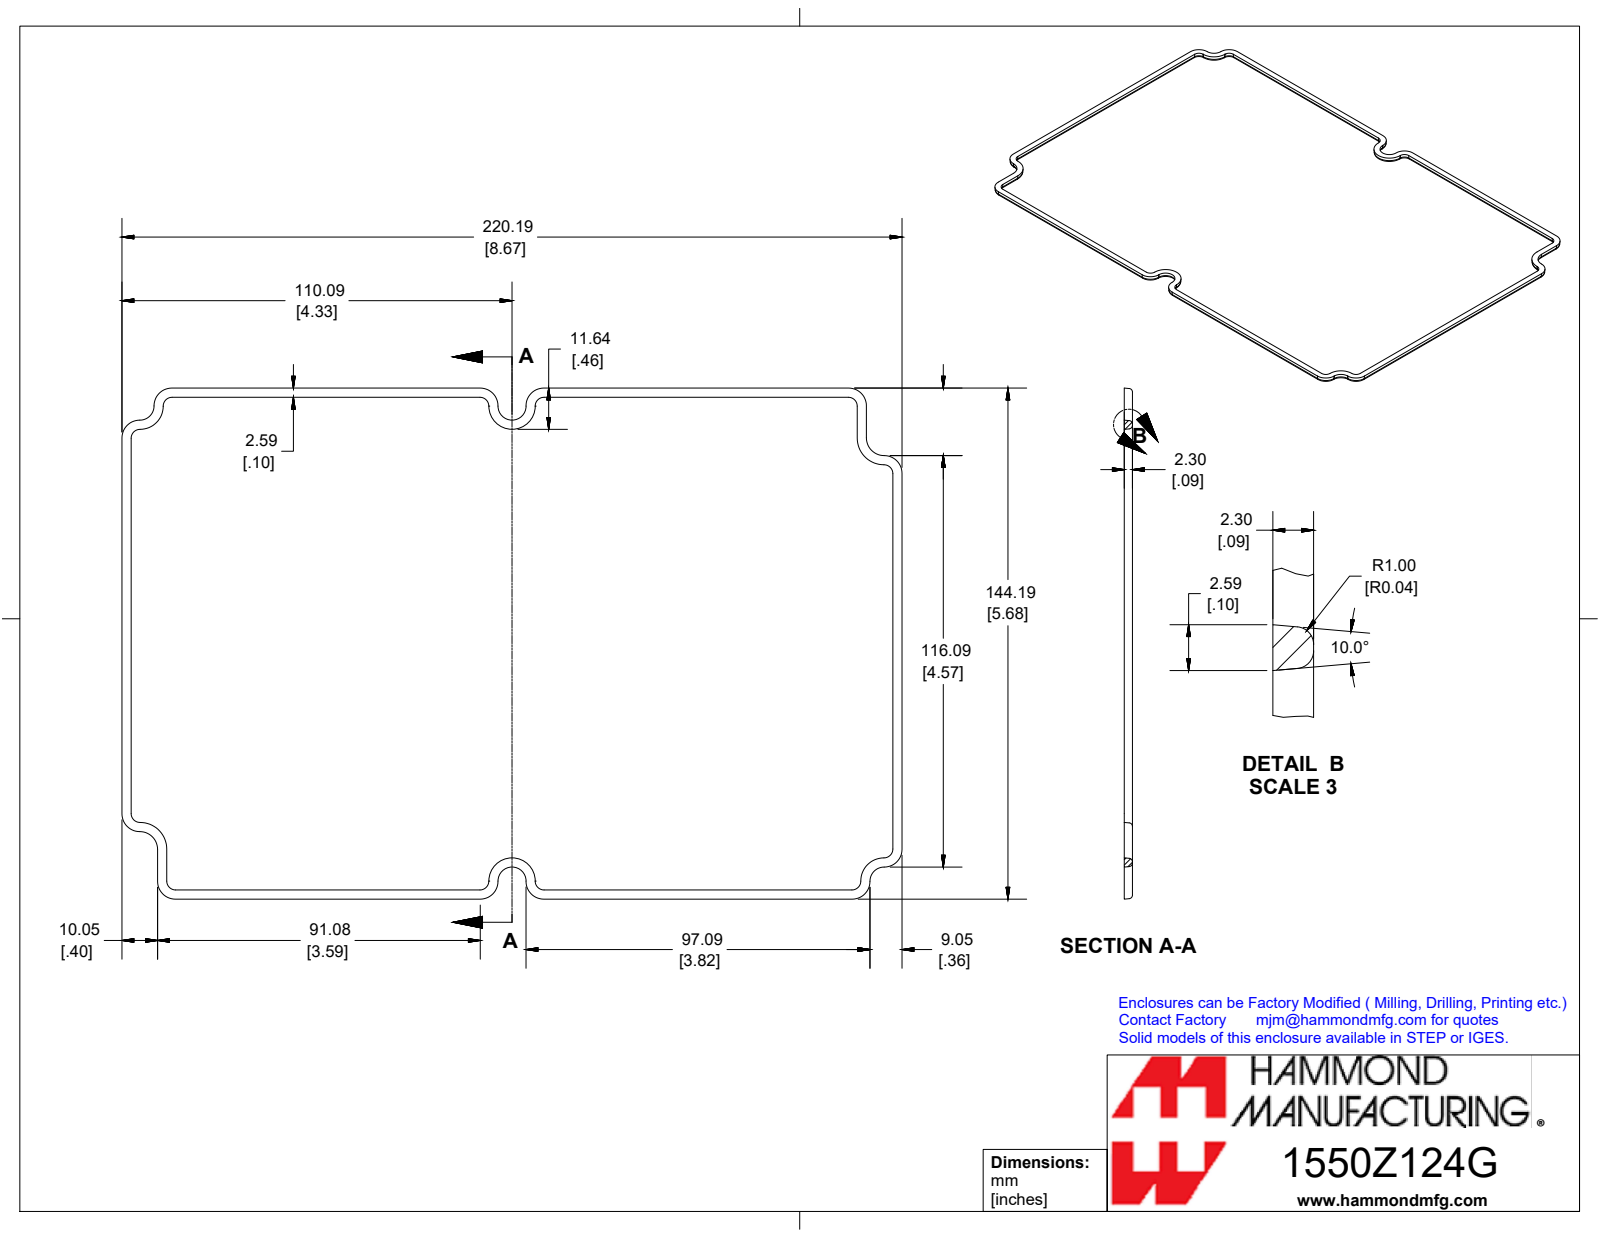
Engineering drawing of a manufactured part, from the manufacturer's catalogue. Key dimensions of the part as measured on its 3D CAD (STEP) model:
Part name (STEP PRODUCT): 1550Z124GASKET
STEP written by: SolidWorks 2019 (CONFIG_CONTROL_DESIGN)
Units: inches
Bodies: 1 solid, 146 faces (38 planar, 36 cylindrical, 72 other)
Overall size (bounding box): 8.669 × 5.677 × 0.091
Volume: 0.225 in³ · Surface area: 9.65 in²
Partial cylindrical surfaces — rounded edges, fillets, slot ends (radius × count): R0.039 ×28
Main face-to-face distances: 5.552, 8.533, 0.091, 0.394, 8.139, 7.744, 4.061, 3.667, 4.472, 4.078
